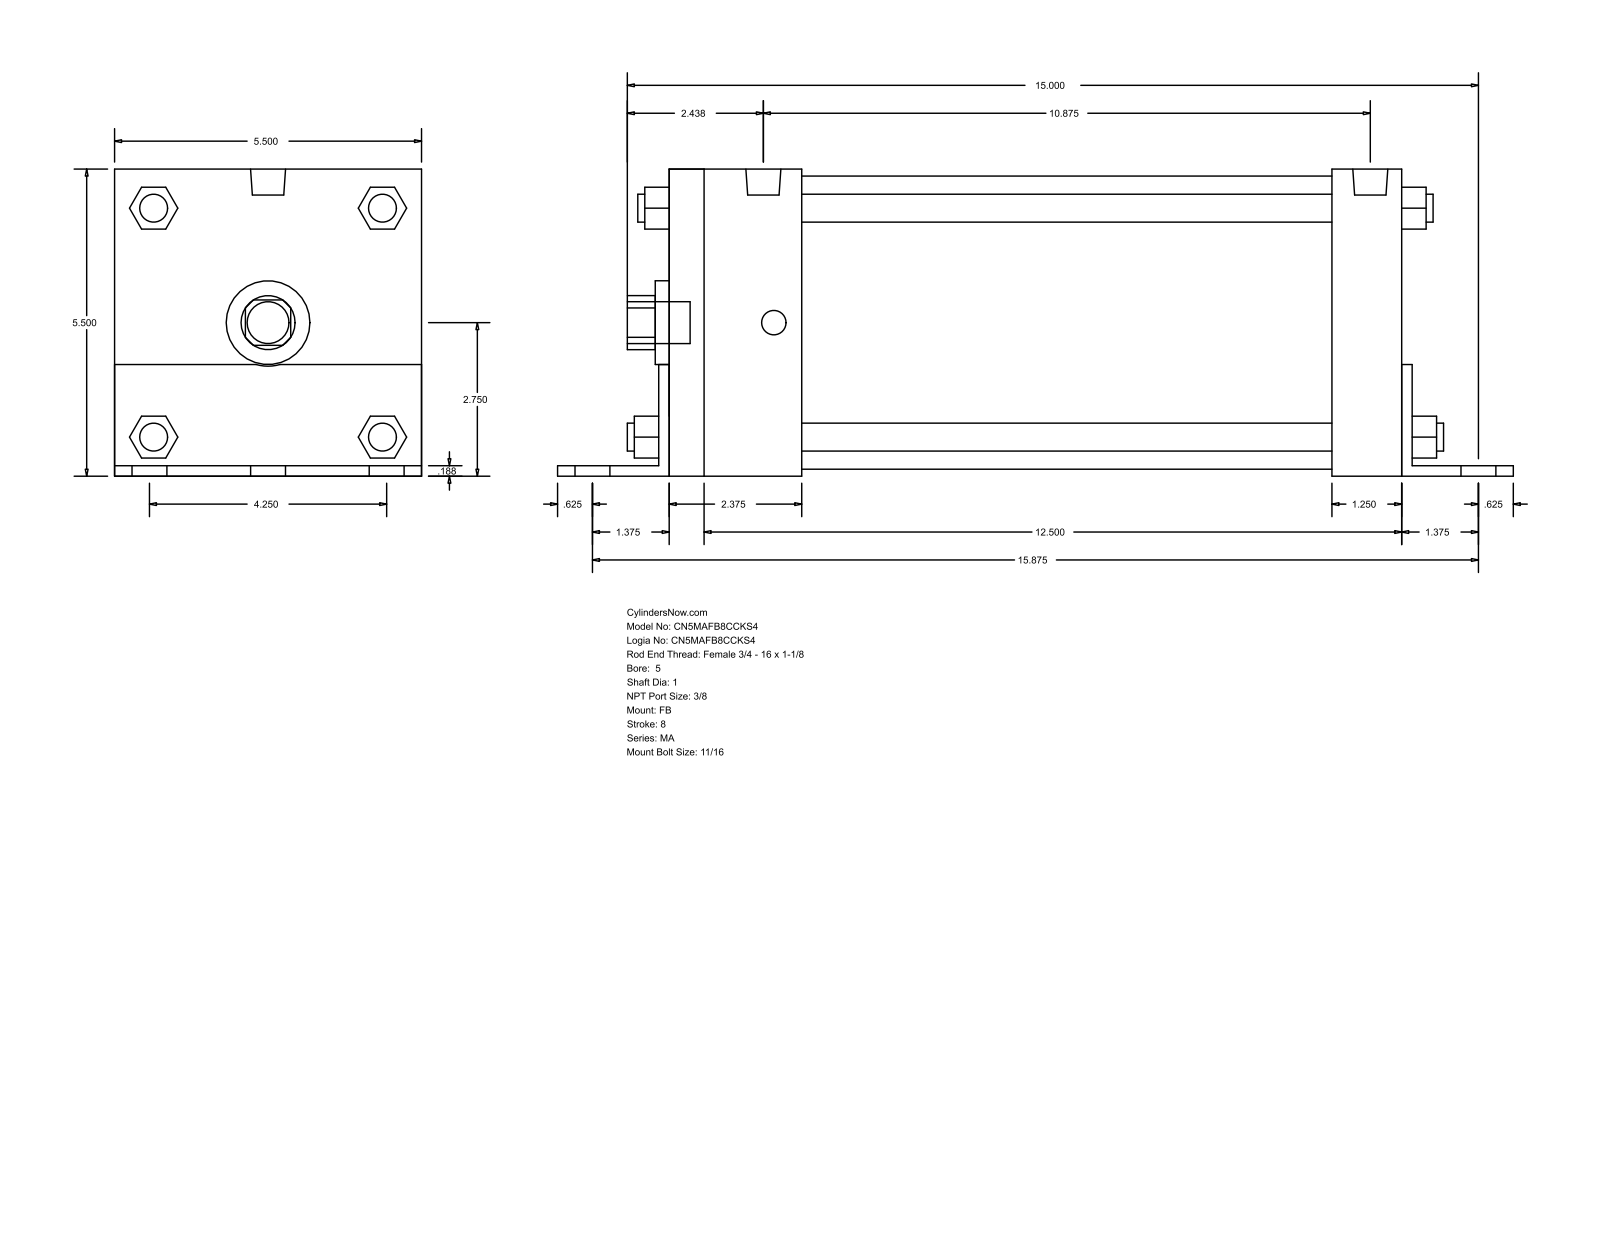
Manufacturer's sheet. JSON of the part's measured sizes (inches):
{"part_name": "MA_FB__0500_1", "step_written_by": "GSSL Pune (CONFIG_CONTROL_DESIGN)", "units": "inches", "bodies": {"solids": 0, "faces": 140, "planar": 105, "cylindrical": 35, "other": 0}, "overall_size": [17.125, 5.502, 5.5], "round_holes": [[1, 1], [1.5, 1], [5.25, 1]], "round_bosses_or_shafts": [[0.687, 6], [0.5, 4], [0.437, 4], [0.627, 2], [0.75, 1]], "partial_cylinders_radius": [[0.484, 1], [0.78, 1]], "face_to_face_distances": [5.5, 0.187, 5.502, 13.313, 0.185, 5.315, 13.125, 13.5, 1.25, 1.437]}
